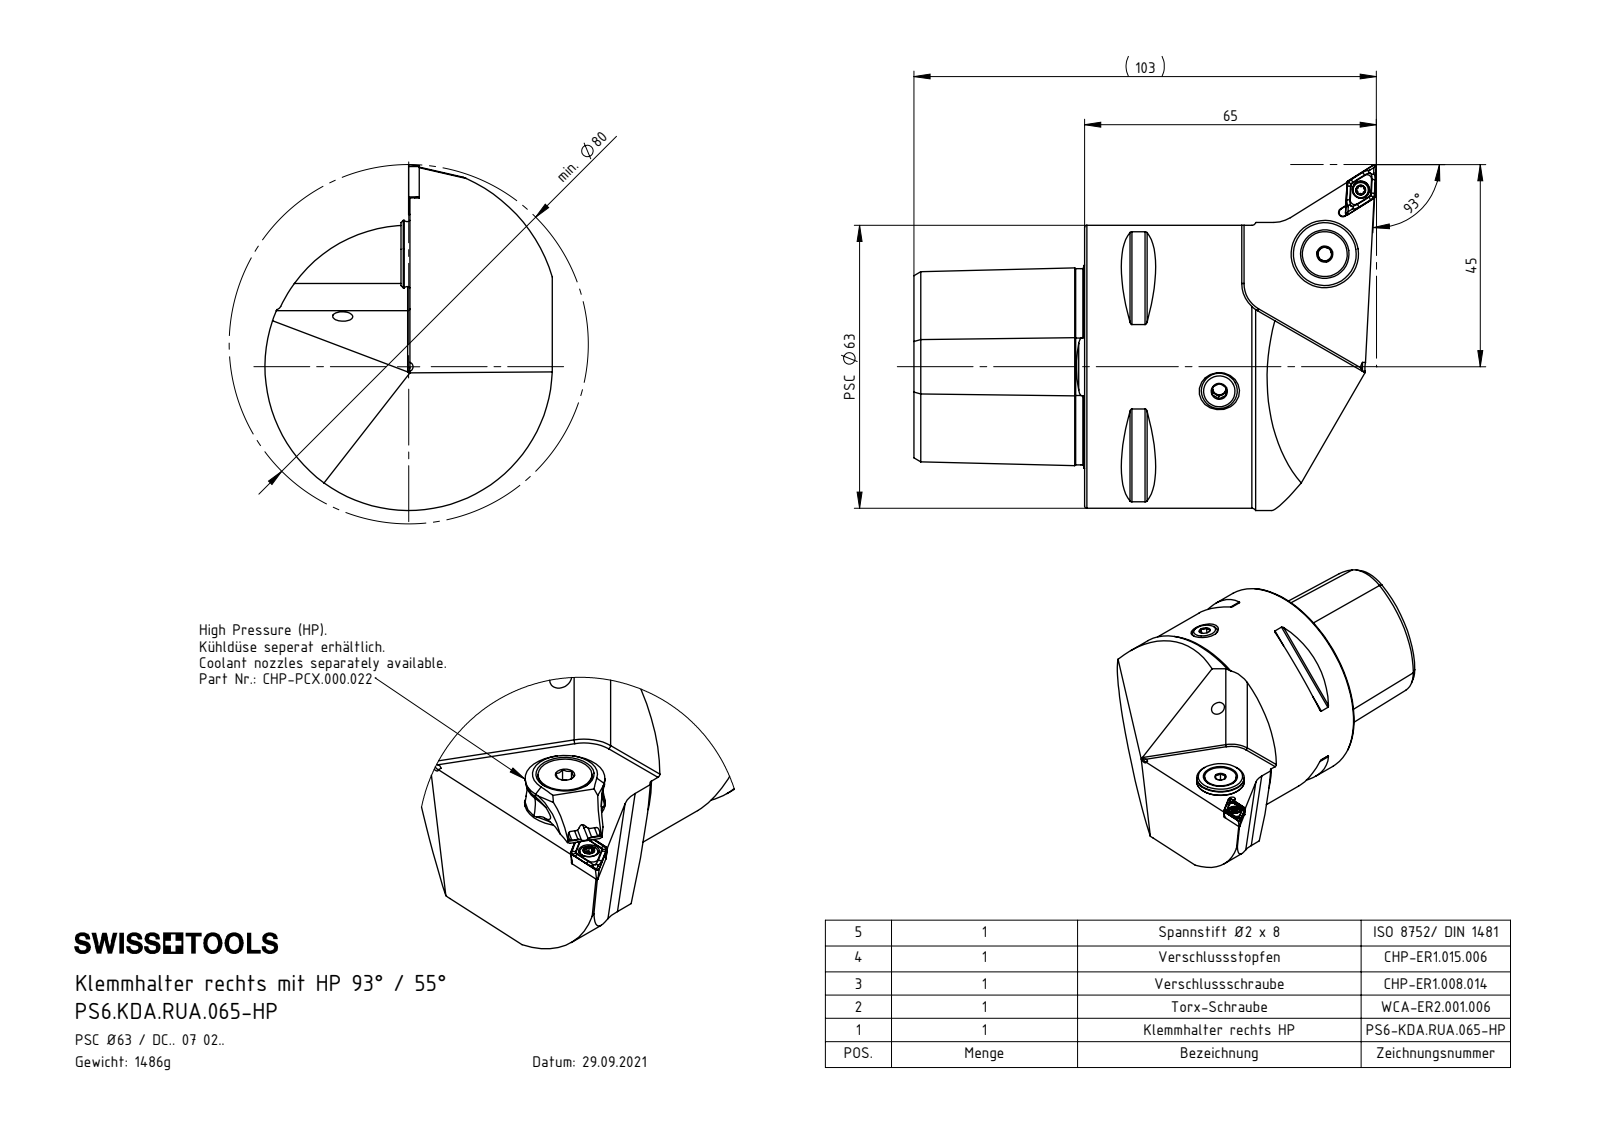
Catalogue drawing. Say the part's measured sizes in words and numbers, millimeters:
The part is named "DIN 3771 - 6.5x1.5; DIN 7991 - M5x18; CHP-ER1.008.014_A; CHP-PCX.000.022_B (+7 more)". Its 3-D file was written by "SolidWorks 2022 (CONFIG_CONTROL_DESIGN)". It is 9 solids with 480 faces: 106 planar, 132 cylindrical and 242 other. Overall it measures 103 by 77 by 64 millimeters. Its volume is 189 782 cubic millimeters and its surface area 32 866 square millimeters. Round holes: 3 of diameter 4.2, 1 of diameter 1.2, 1 of diameter 2, 1 of diameter 2.05, 1 of diameter 2.8, 1 of diameter 3, 1 of diameter 3.85, 1 of diameter 5, 1 of diameter 5.3, 1 of diameter 7, 1 of diameter 8.1, 1 of diameter 10. Round bosses or shafts: 1 of diameter 63, 1 of diameter 14.85, 1 of diameter 13.4, 1 of diameter 10, 1 of diameter 8, 1 of diameter 5.5, 1 of diameter 5, 1 of diameter 3.4. Partial cylindrical surfaces (rounded edges, fillets, slot ends): 12 of radius 0.5, 8 of radius 1, 6 of radius 0.21, 4 of radius 0.36, 4 of radius 6, 2 of radius 0.36, 2 of radius 1.1, 2 of radius 1.2. The main face-to-face distances are 38, 31.7, 24.88, 11, 27, 73, 46, 35, 55.8, 27.2. The hole center spacings are 4.5, 13.1, 13.21, 16.34, 16.45, 27.5, 48.49, 50.37.
